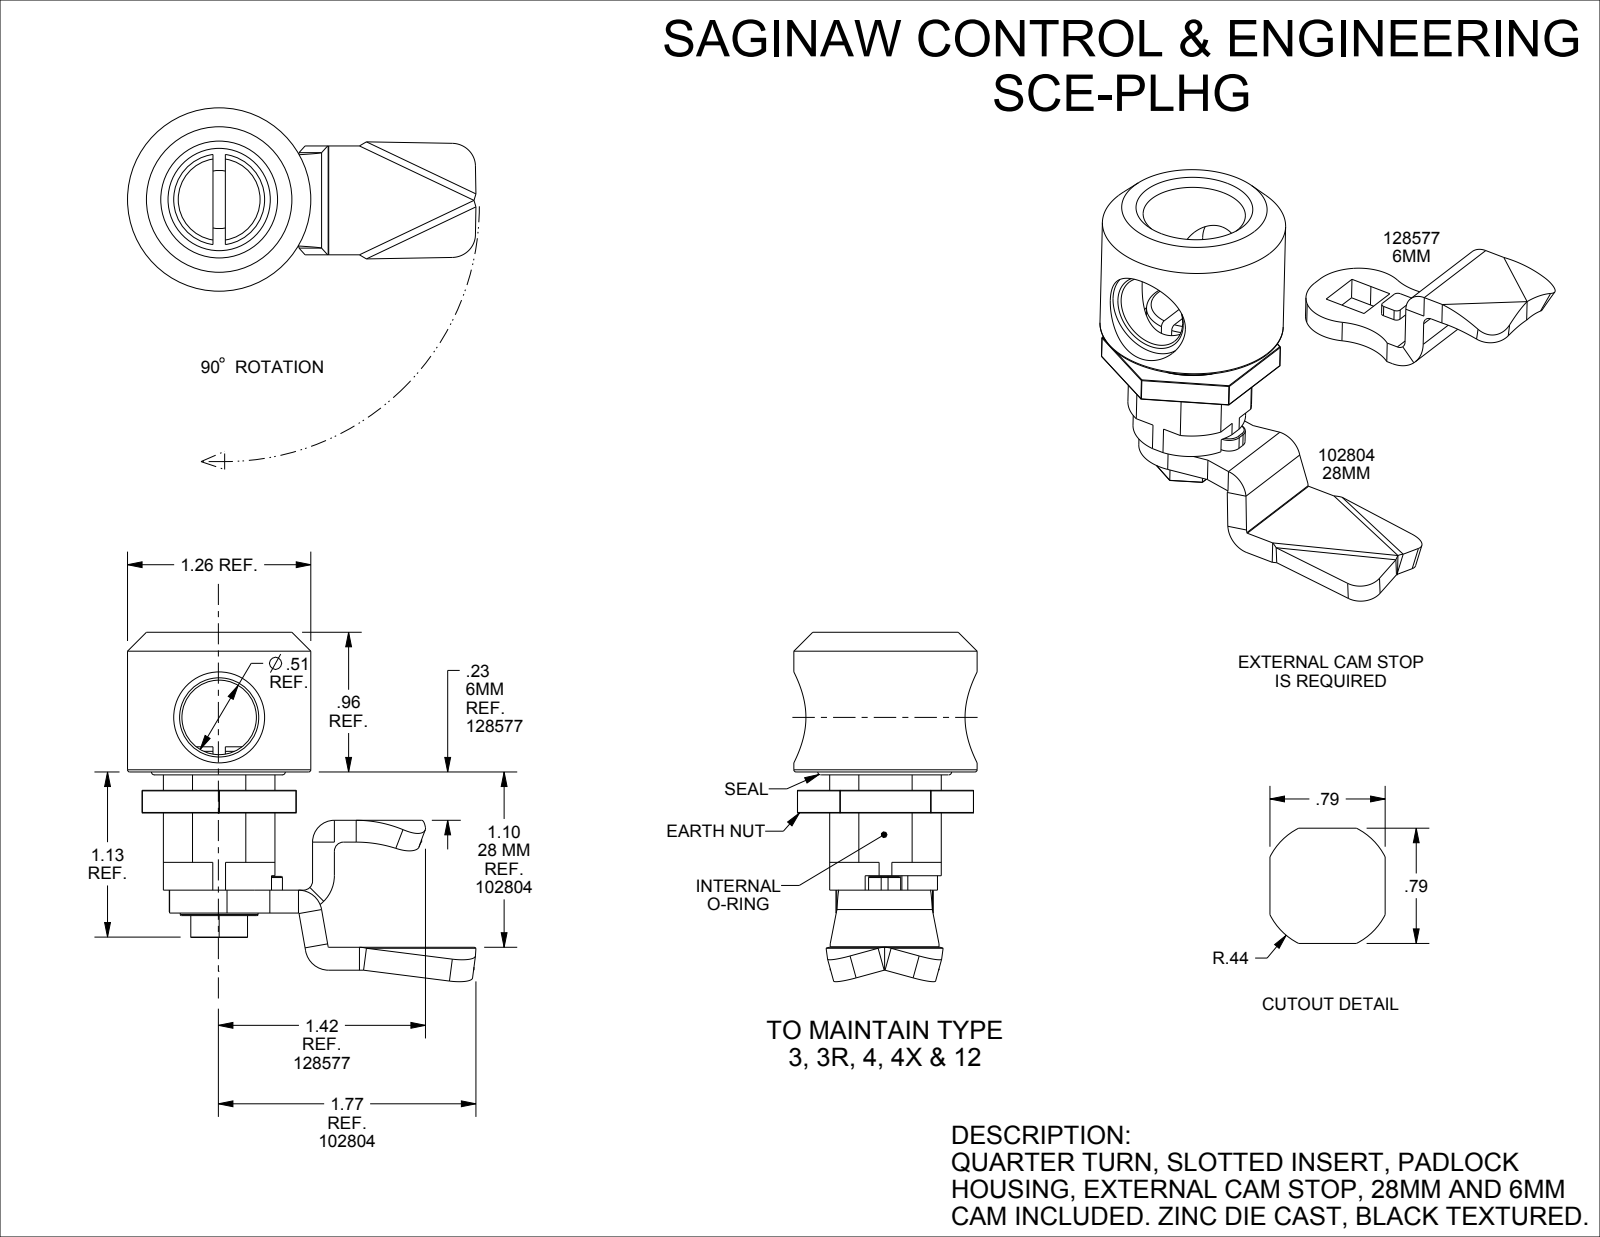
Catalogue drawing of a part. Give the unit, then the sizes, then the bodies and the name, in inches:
Units: inches
Overall size (bounding box): 3.105 × 2.401 × 2.395
Round holes (diameter × count): ⌀0.225 ×1, ⌀0.3 ×1, ⌀0.4 ×1, ⌀0.405 ×1, ⌀0.512 ×1, ⌀0.625 ×1, ⌀0.703 ×1, ⌀0.851 ×1
Round bosses / shafts (diameter × count): ⌀1.26 ×1, ⌀0.772 ×1, ⌀0.625 ×1, ⌀0.535 ×1, ⌀0.5 ×1, ⌀0.381 ×1, ⌀0.225 ×1
Partial cylindrical surfaces — rounded edges, fillets, slot ends (radius × count): R0.005 ×16, R0.03 ×4, R0.157 ×4, R0.3 ×4, R0.004 ×2, R0.008 ×2, R0.02 ×2, R0.087 ×2
Main face-to-face distances: 0.157, 0.15, 0.393, 0.812, 0.55, 0.53, 0.48, 0.282, 0.767, 1.362
Volume: 1.695 in³ · Surface area: 24.8 in²
Bodies: 8 solids, 282 faces (131 planar, 110 cylindrical, 41 other)
Part name (STEP PRODUCT): SCE-PLHG
STEP written by: SolidWorks 2019 (CONFIG_CONTROL_DESIGN)
